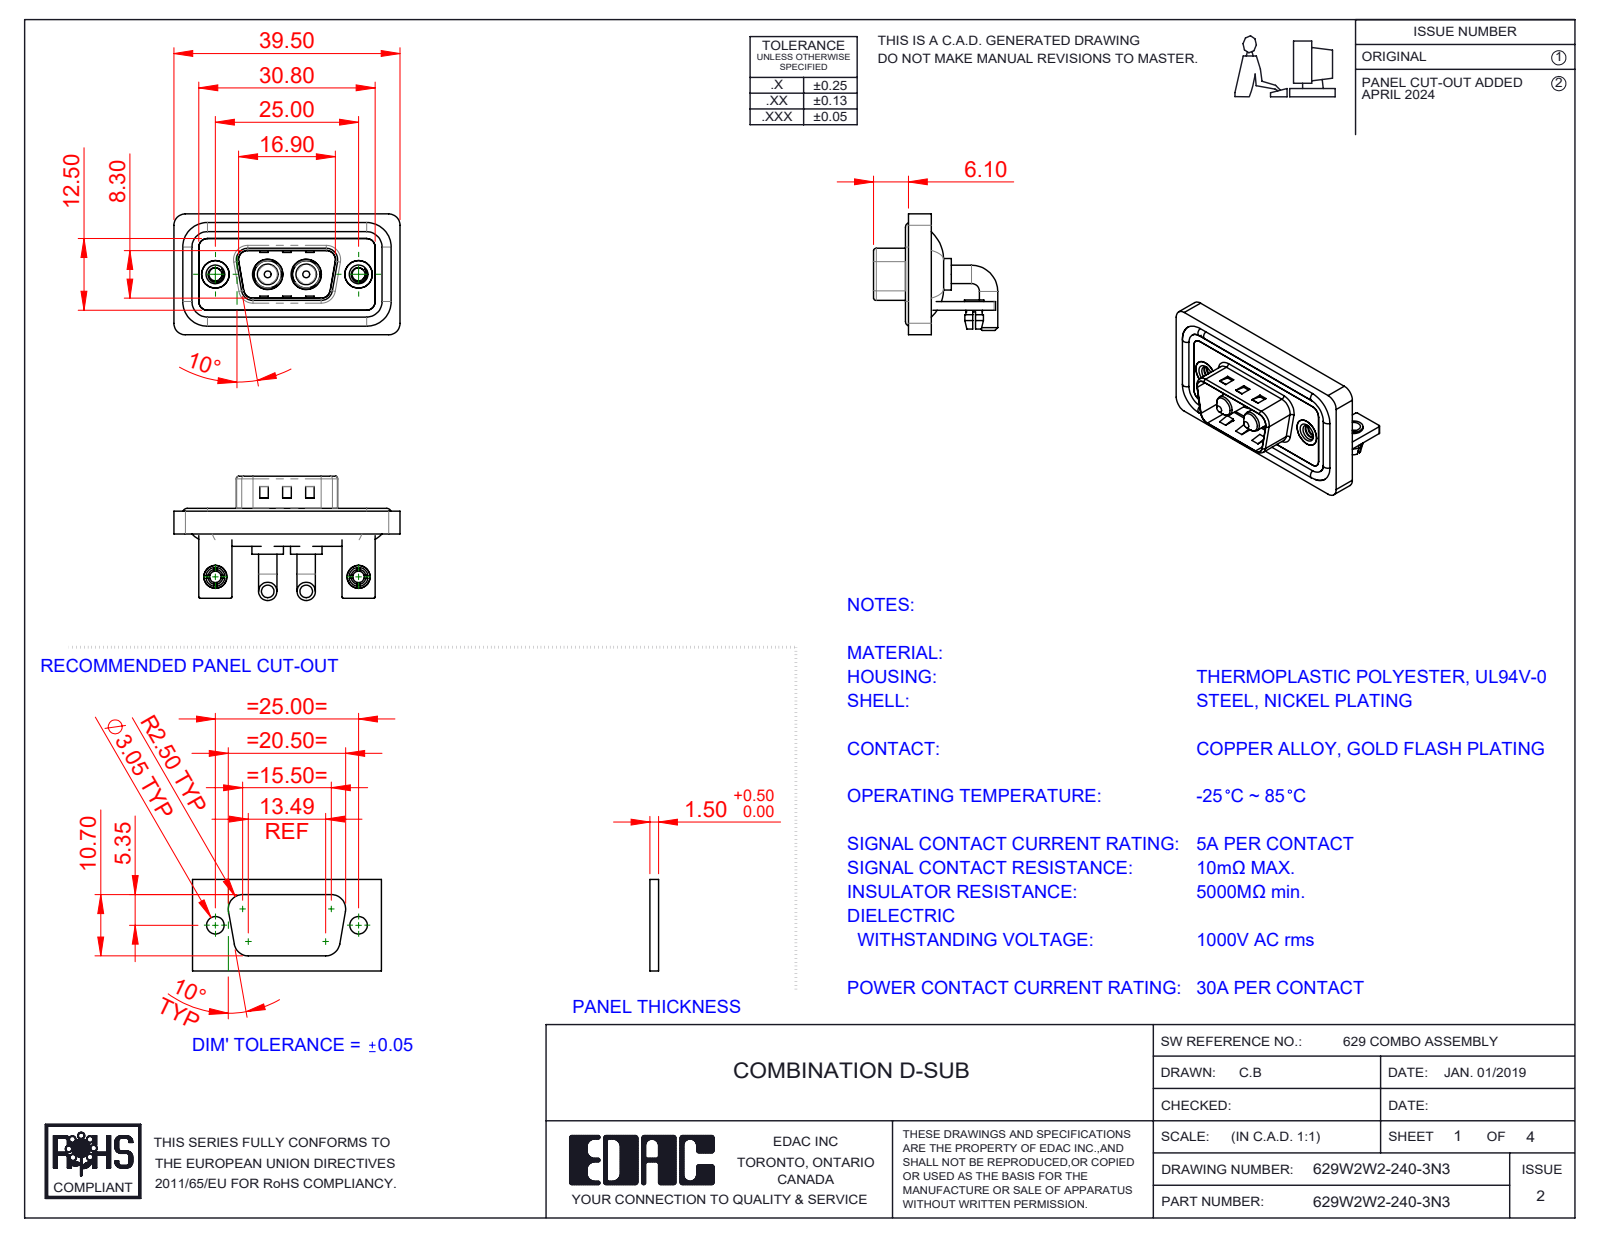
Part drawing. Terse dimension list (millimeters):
name: 629Combo Threaded Rivet_3; Power Pin_30A RA; 629Combo Shell Front_09 Contacts; 629W2W2-240-3N3 (+5 more)
written by: SolidWorks 2023 (CONFIG_CONTROL_DESIGN)
unit: mm
bodies: 15 solids, 629 faces (233 planar, 272 cylindrical, 124 other)
size: 39.5 × 21.7 × 21.1
volume: 4 954 mm³; area: 8 001 mm²
holes: 2× ⌀2, 2× ⌀2.26, 2× ⌀2.5, 2× ⌀3.2, 2× ⌀4, 2× ⌀4.8, 2× ⌀4.85, 2× ⌀5, 2× ⌀5.3
bosses: 4× ⌀3.2, 4× ⌀1.6, 2× ⌀5.5, 2× ⌀5.2, 2× ⌀4.9, 2× ⌀4.75, 2× ⌀4, 2× ⌀3.75
rounds: 19× R2, 18× R1.5, 16× R0.25, 9× R0.5, 8× R1.6, 4× R0.6, 4× R0.65, 4× R0.9
face distances: 0.4, 1.5, 2.9, 0.8, 1.1, 1.2, 2.1, 1.6, 3.7, 2.5
hole spacings: 9.14, 15.86, 25, 6.72
